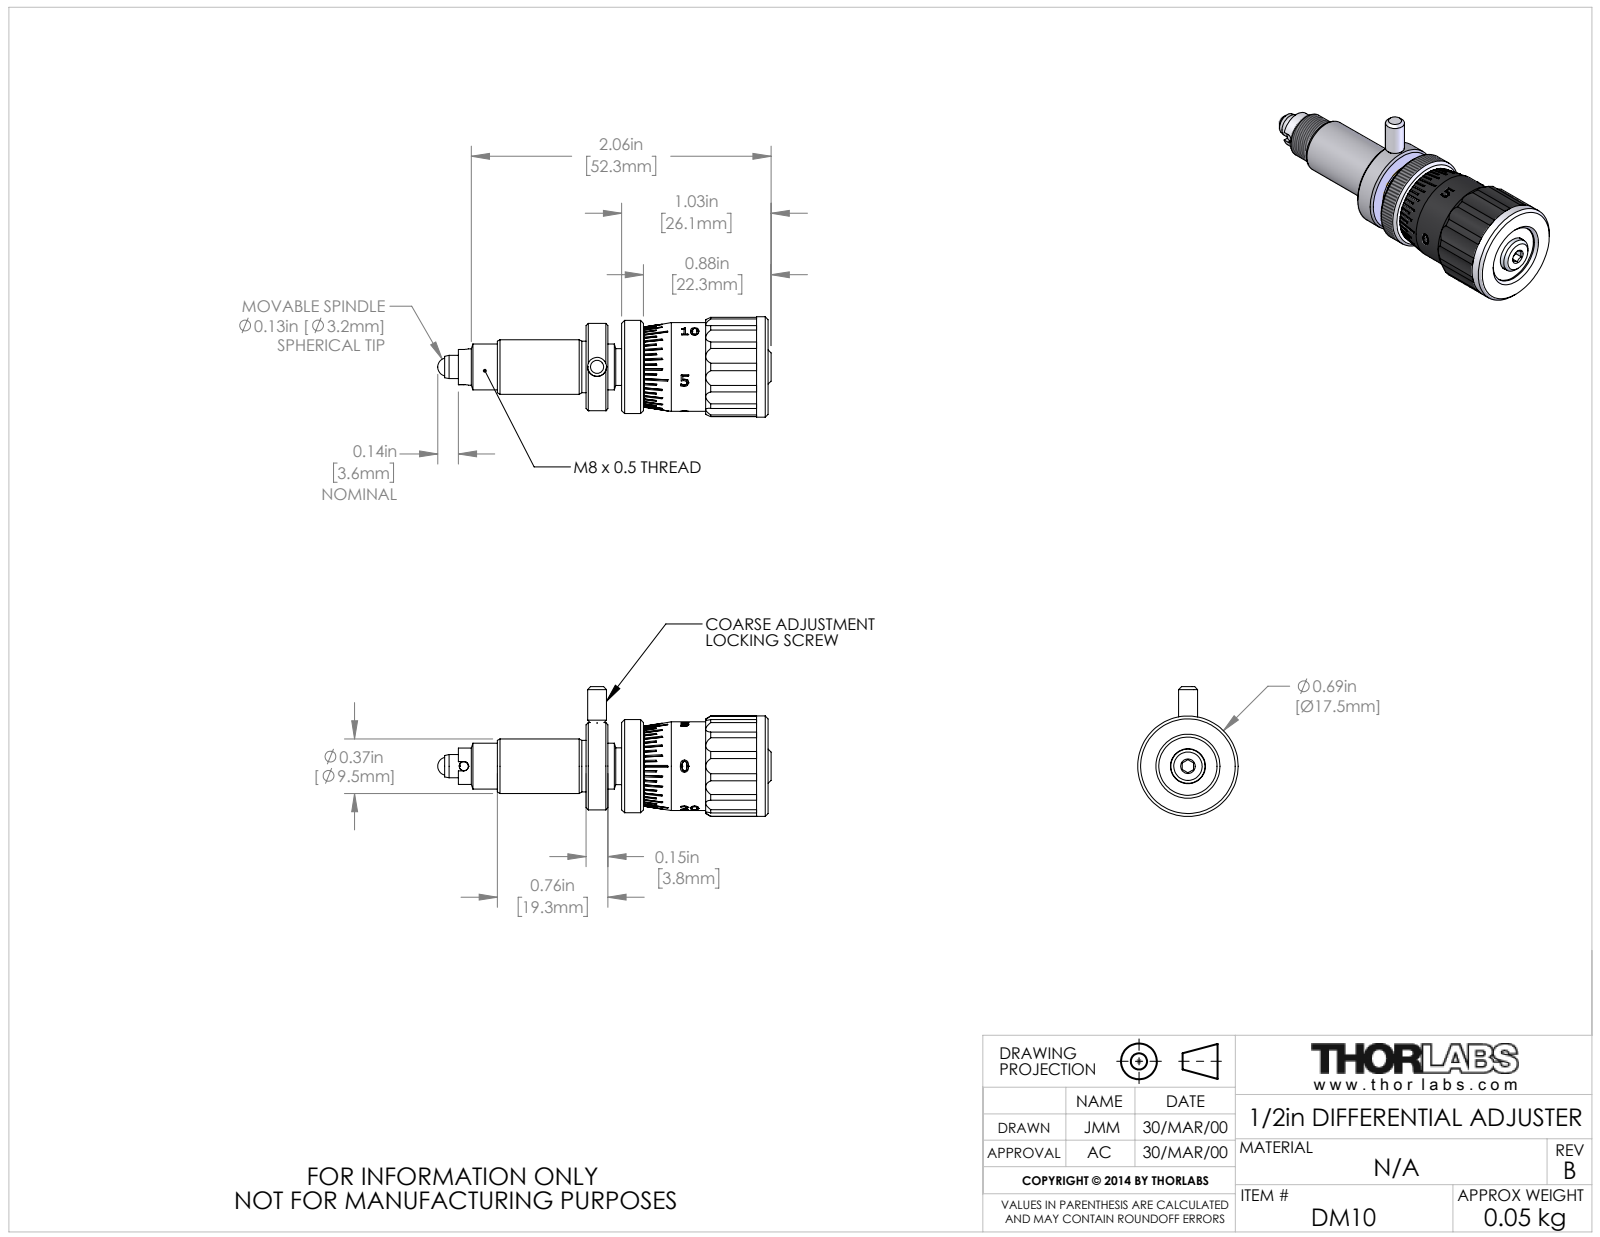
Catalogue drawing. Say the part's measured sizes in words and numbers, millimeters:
The part is named "3112-E0W". Its 3-D file was written by "SolidWorks 2018 (AUTOMOTIVE_DESIGN)". It is 13 solids with 614 faces: 265 planar, 151 cylindrical and 198 other. Overall it measures 58.21 by 22.65 by 17.53 millimeters. Its volume is 7 015 cubic millimeters and its surface area 9 414 square millimeters. Round holes: 1 of diameter 1.59, 1 of diameter 1.6, 1 of diameter 1.78, 1 of diameter 2.69, 1 of diameter 3.18, 1 of diameter 3.5, 1 of diameter 3.51, 1 of diameter 3.56, 1 of diameter 4.06, 1 of diameter 4.32, 1 of diameter 4.76, 1 of diameter 6. Round bosses or shafts: 1 of diameter 17.53, 1 of diameter 16.26, 1 of diameter 15.49, 1 of diameter 15.24, 1 of diameter 12.57, 1 of diameter 12.55, 1 of diameter 11.18, 1 of diameter 9.65. Partial cylindrical surfaces (rounded edges, fillets, slot ends): 14 of radius 2.38, 1 of radius 0.8, 1 of radius 7.76. The main face-to-face distances are 3.81, 6.19, 2.03, 7.24, 16.31, 23.55, 2.38, 18.69, 25.93, 27.96.
